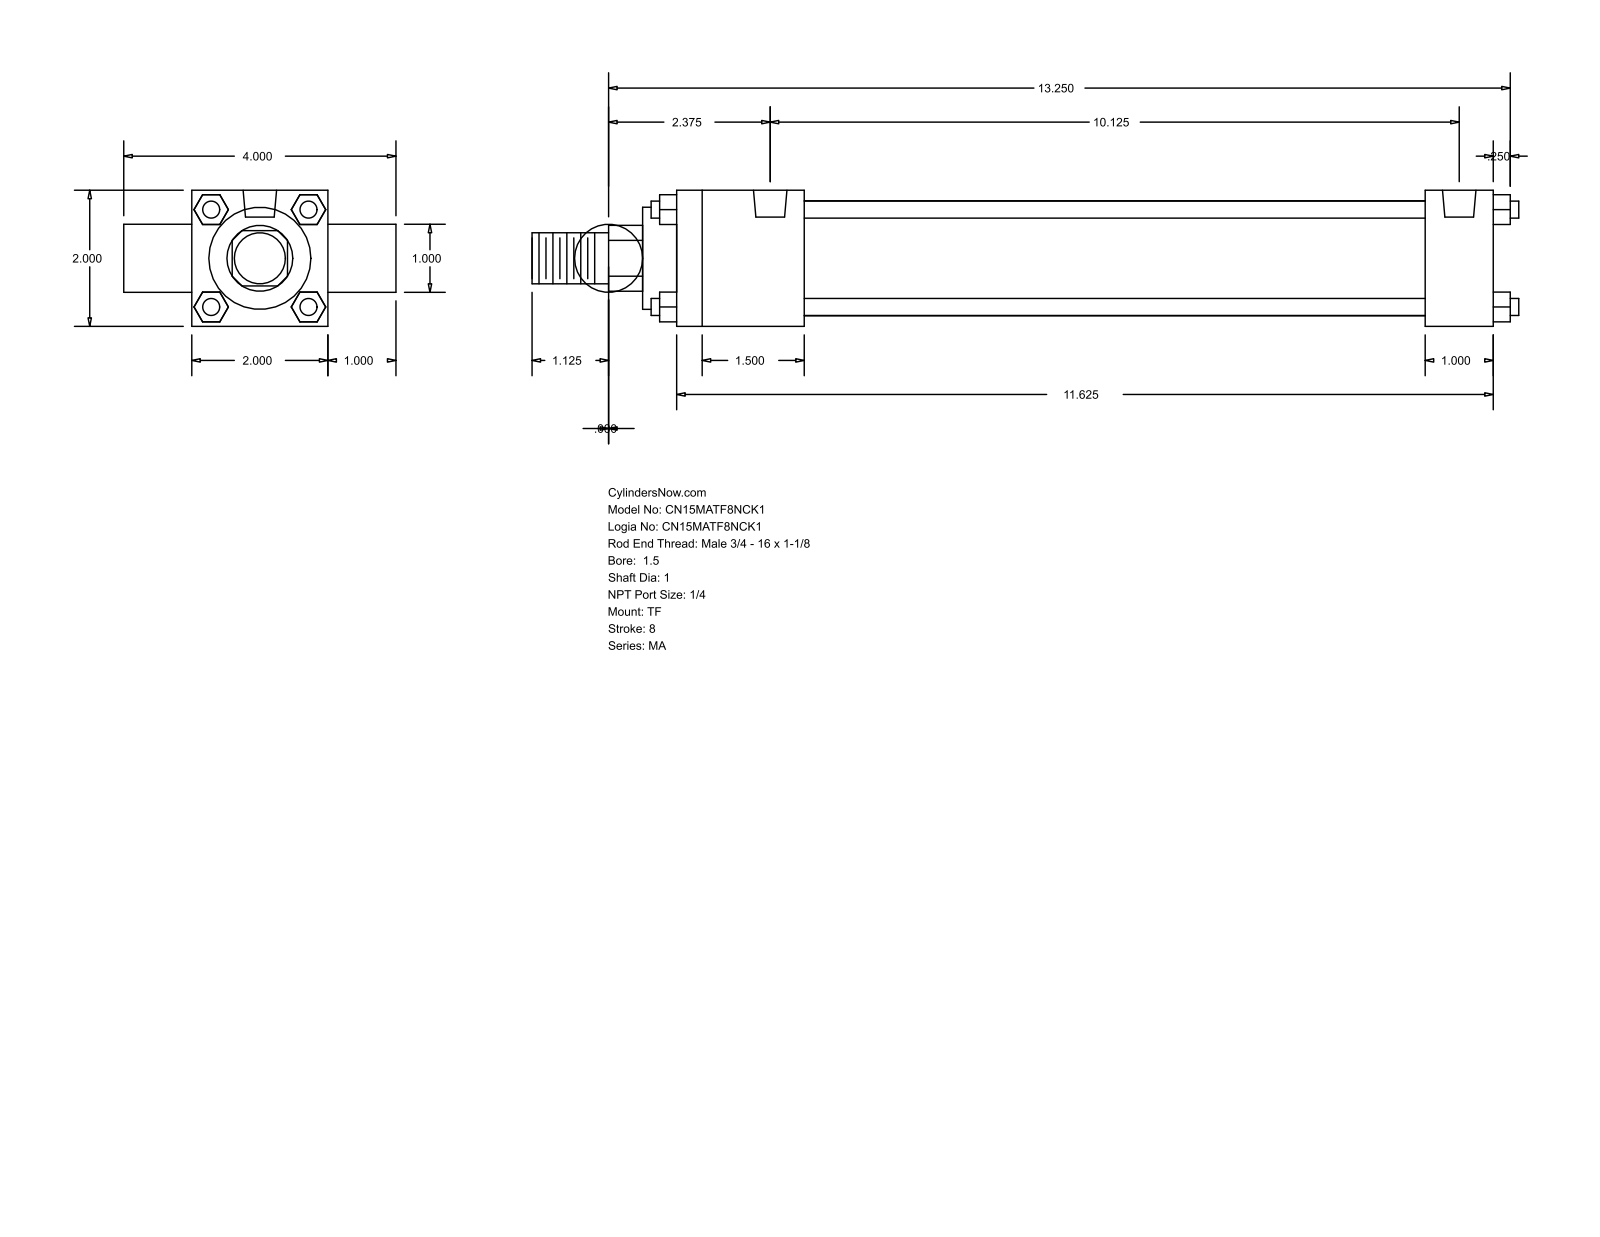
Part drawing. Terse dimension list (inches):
name: MA_TF__0150_1
written by: GSSL Pune (CONFIG_CONTROL_DESIGN)
unit: in
bodies: 0 solids, 120 faces (92 planar, 28 cylindrical, 0 other)
size: 14.5 × 4 × 2
holes: 3× ⌀0.313, 2× ⌀0.492
bosses: 4× ⌀0.25, 2× ⌀1, 1× ⌀1.69, 1× ⌀1.5, 1× ⌀0.75
rounds: 1× R0.484
face distances: 2, 1, 12, 3, 0.25, 1.875, 11, 9.125, 10.125, 12.5
hole spacings: 10.125
